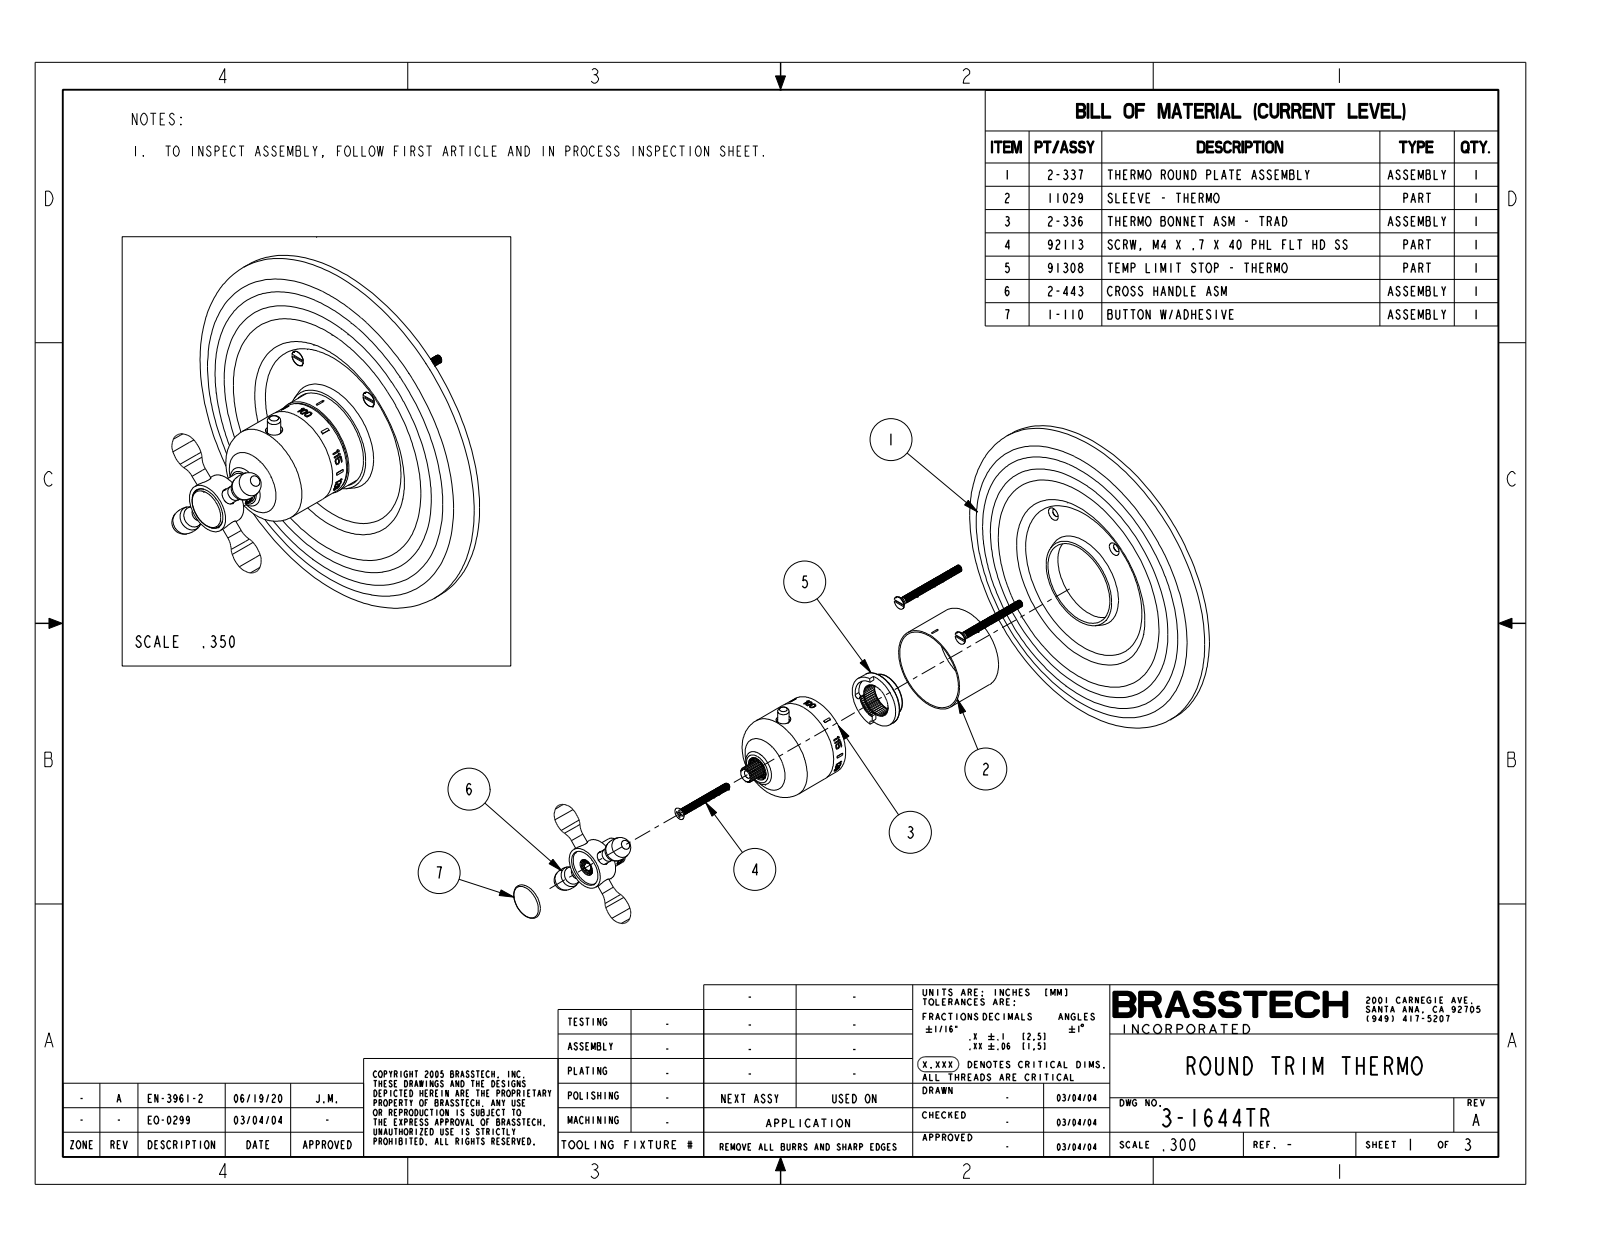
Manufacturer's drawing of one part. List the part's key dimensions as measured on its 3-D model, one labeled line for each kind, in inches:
Part name (STEP PRODUCT): 3-1644TR
STEP written by: CREO PARAMETRIC BY PTC INC, 2018400 (CONFIG_CONTROL_DESIGN)
Units: inches
Bodies: 1 solid, 449 faces (330 planar, 47 cylindrical, 72 other)
Overall size (bounding box): 7.5 × 7.5 × 3.877
Volume: 25.5 in³ · Surface area: 119.3 in²
Round holes (diameter × count): ⌀0.313 ×1
Round bosses / shafts (diameter × count): ⌀0.3 ×2, ⌀7.5 ×1, ⌀1.97 ×1, ⌀1.94 ×1, ⌀1.929 ×1, ⌀1 ×1, ⌀0.625 ×1, ⌀0.26 ×1
Partial cylindrical surfaces — rounded edges, fillets, slot ends (radius × count): R0.969 ×1
Main face-to-face distances: 0.313, 0.159, 0.471, 3.756, 3.444, 3.285, 0.863, 0.55, 0.391, 2.894
